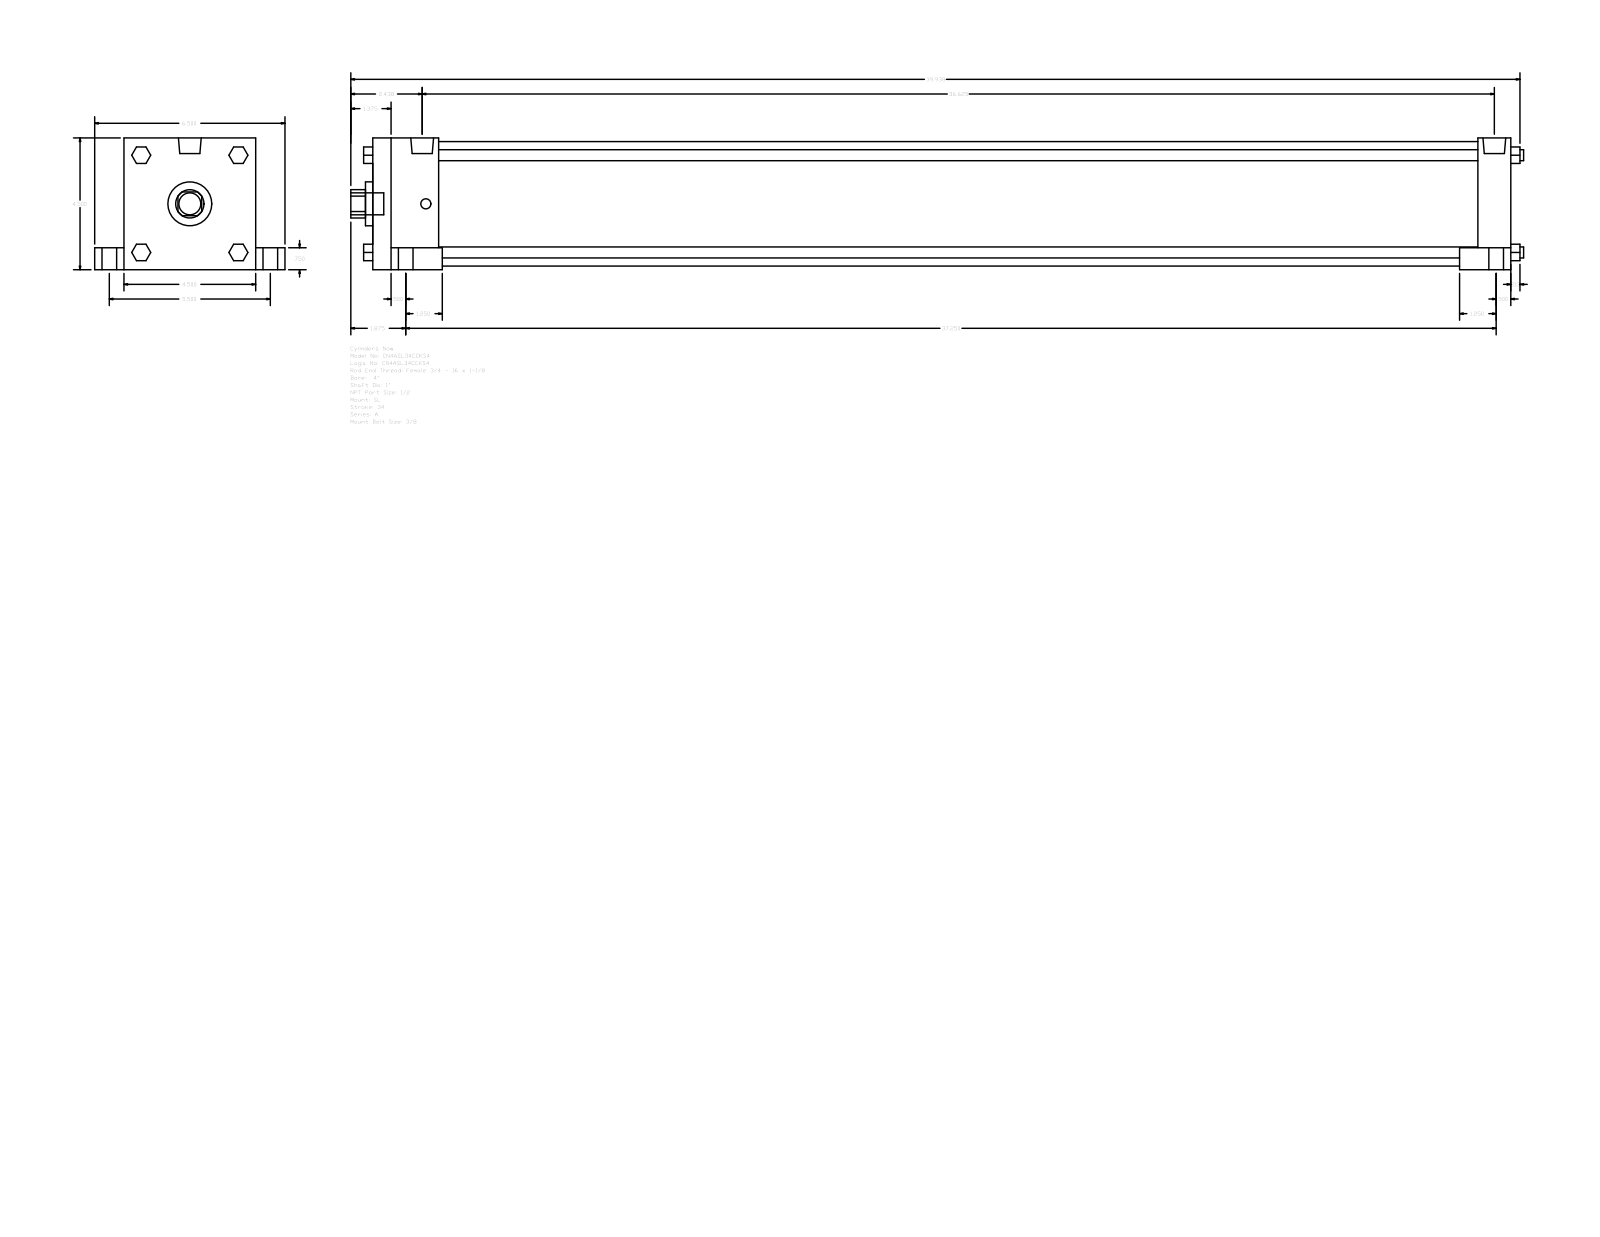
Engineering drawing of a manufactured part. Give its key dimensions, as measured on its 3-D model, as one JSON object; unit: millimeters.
{"part_name": "A_SL__0400_1", "step_written_by": "GSSL Pune (CONFIG_CONTROL_DESIGN)", "units": "millimeters", "bodies": {"solids": 0, "faces": 150, "planar": 114, "cylindrical": 36, "other": 0}, "overall_size": [1017.59, 165.1, 114.3], "round_holes": [[25.4, 1], [38.1, 1], [107.95, 1]], "round_bosses_or_shafts": [[19.05, 5], [12.7, 4], [9.53, 4], [8.73, 4], [19.77, 2]], "partial_cylinders_radius": [[12.29, 1]], "face_to_face_distances": [114.3, 987.43, 57.15, 930.28, 958.85, 901.7, 28.58, 19.05, 25.4, 139.7]}
